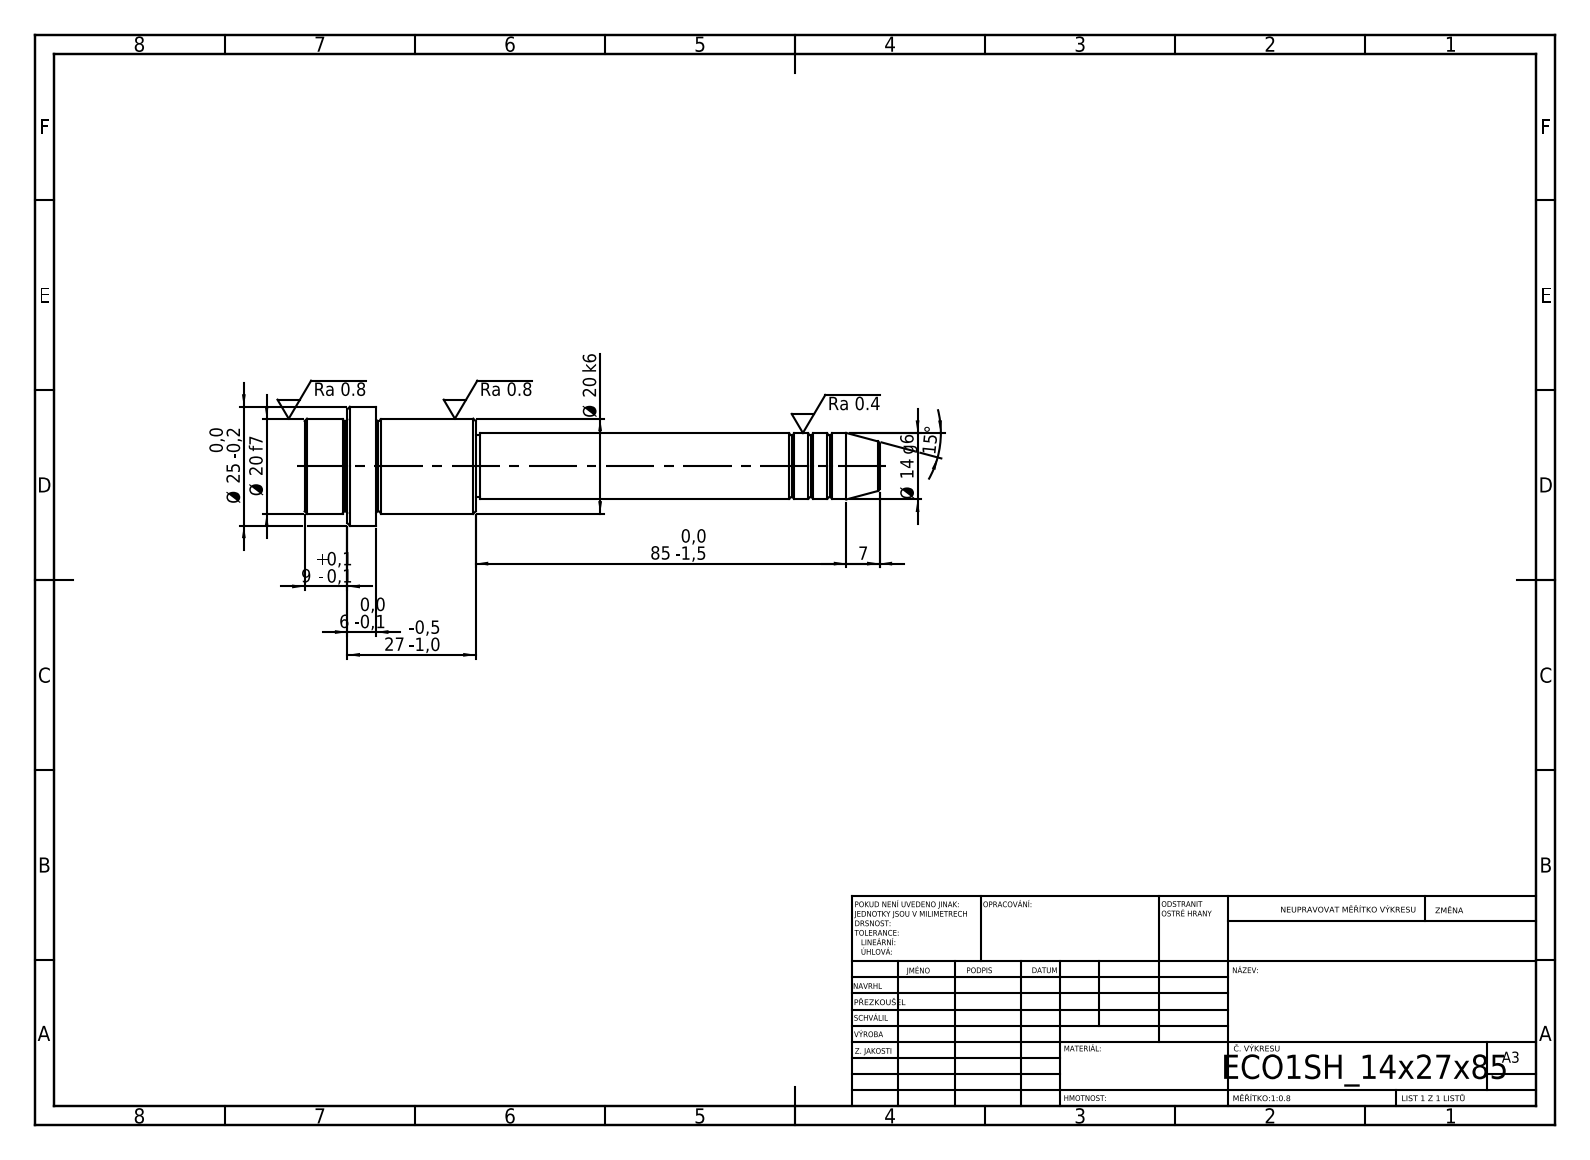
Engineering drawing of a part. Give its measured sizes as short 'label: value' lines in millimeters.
written by: SolidWorks 2019 (CONFIG_CONTROL_DESIGN)
unit: mm
bodies: 1 solid, 52 faces (6 planar, 16 cylindrical, 30 other)
size: 121 × 25 × 25
volume: 25 046 mm³; area: 7 079 mm²
bosses: 1× ⌀25, 1× ⌀20, 1× ⌀14, 1× ⌀13
face distances: 15, 21, 36, 27, 6, 9, 85, 106, 112, 121
